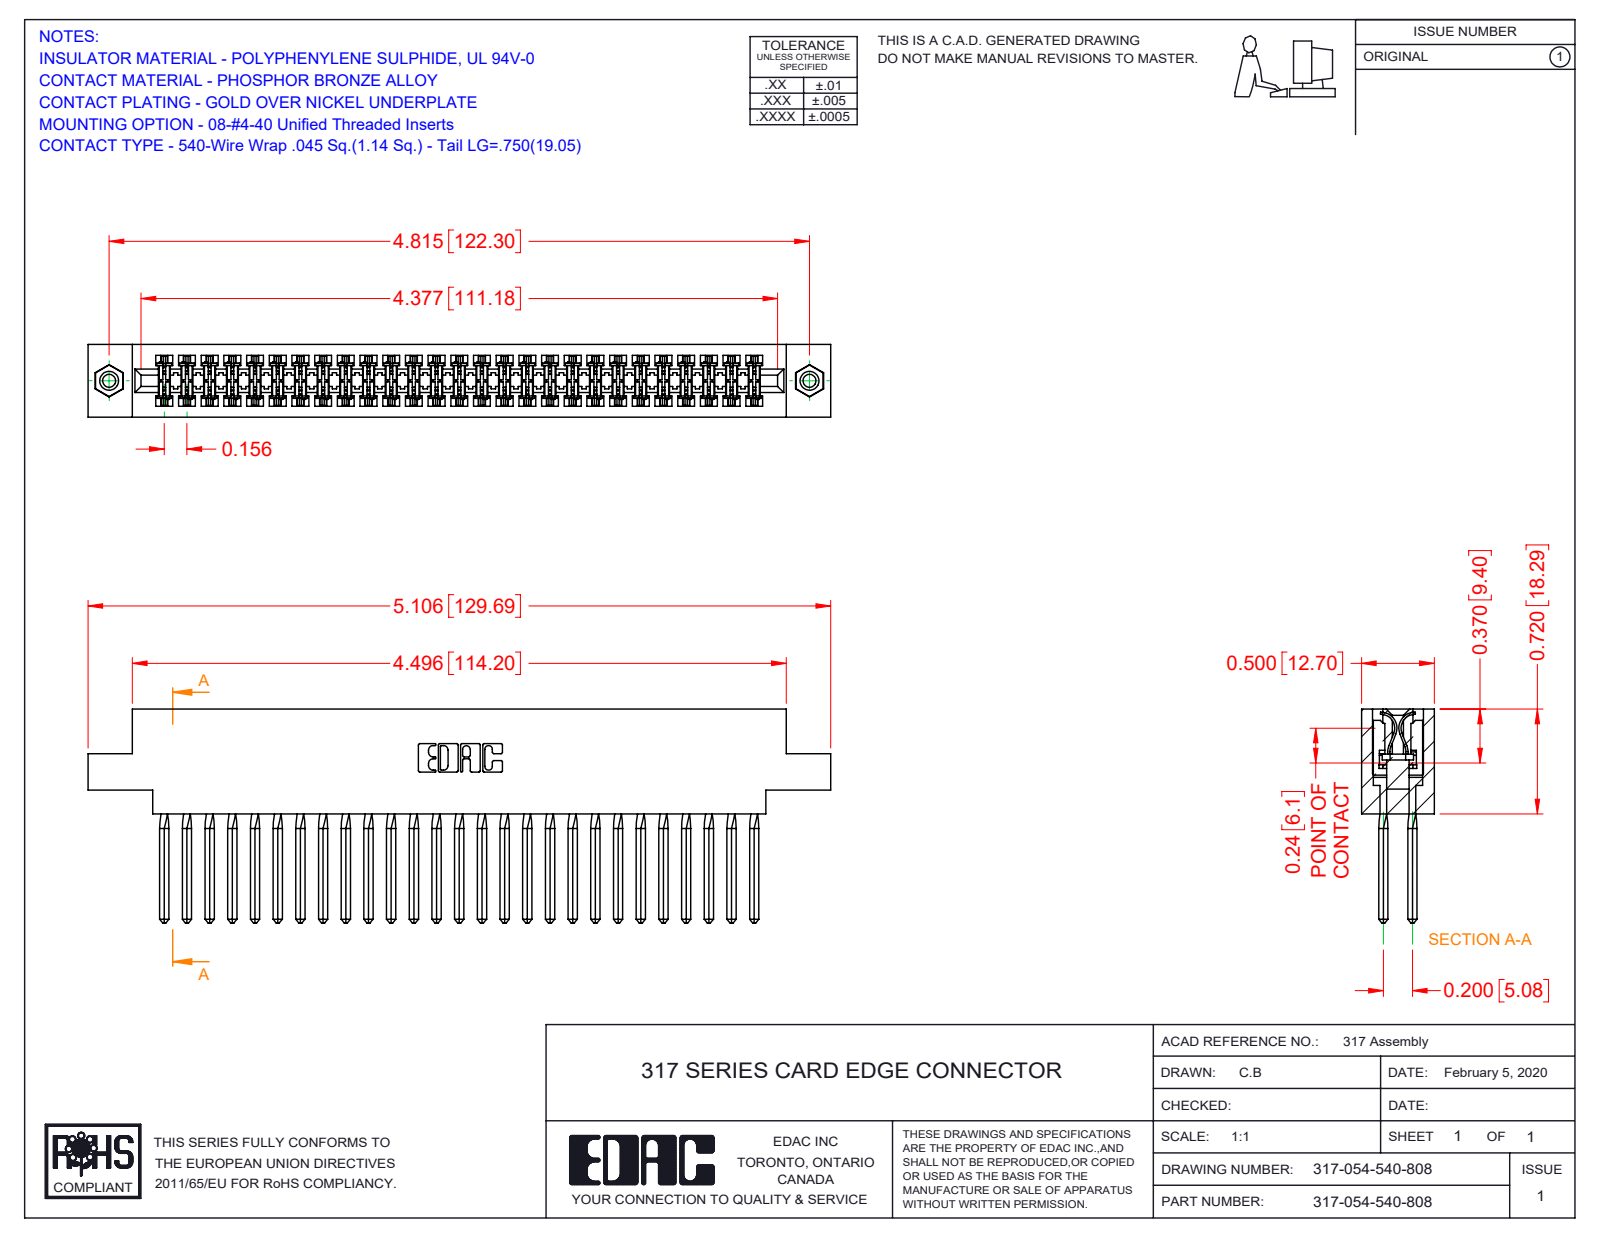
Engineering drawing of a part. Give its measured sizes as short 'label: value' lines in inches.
name: 345-250-001_345-250-003-102; 317-054-540-878; 317 Part_.156 Dia - TI; 317-290-001_540
written by: SolidWorks 2016 (CONFIG_CONTROL_DESIGN)
unit: in
bodies: 57 solids, 4968 faces (4032 planar, 704 cylindrical, 232 other)
size: 5.106 × 1.47 × 0.5
volume: 1.297 in³; area: 48.27 in²
holes: 2× ⌀0.089, 2× ⌀0.125, 2× ⌀0.156
bosses: 2× ⌀0.155
rounds: 108× R0.015, 22× R0.01, 6× R0.007, 6× R0.031, 3× R0.026, 2× R0.095, 2× R0.1, 2× R0.11
face distances: 0.5, 0.075, 0.425, 0.35, 0.11, 0.195, 0.094, 0.2, 0.72, 0.115
hole spacings: 4.815
